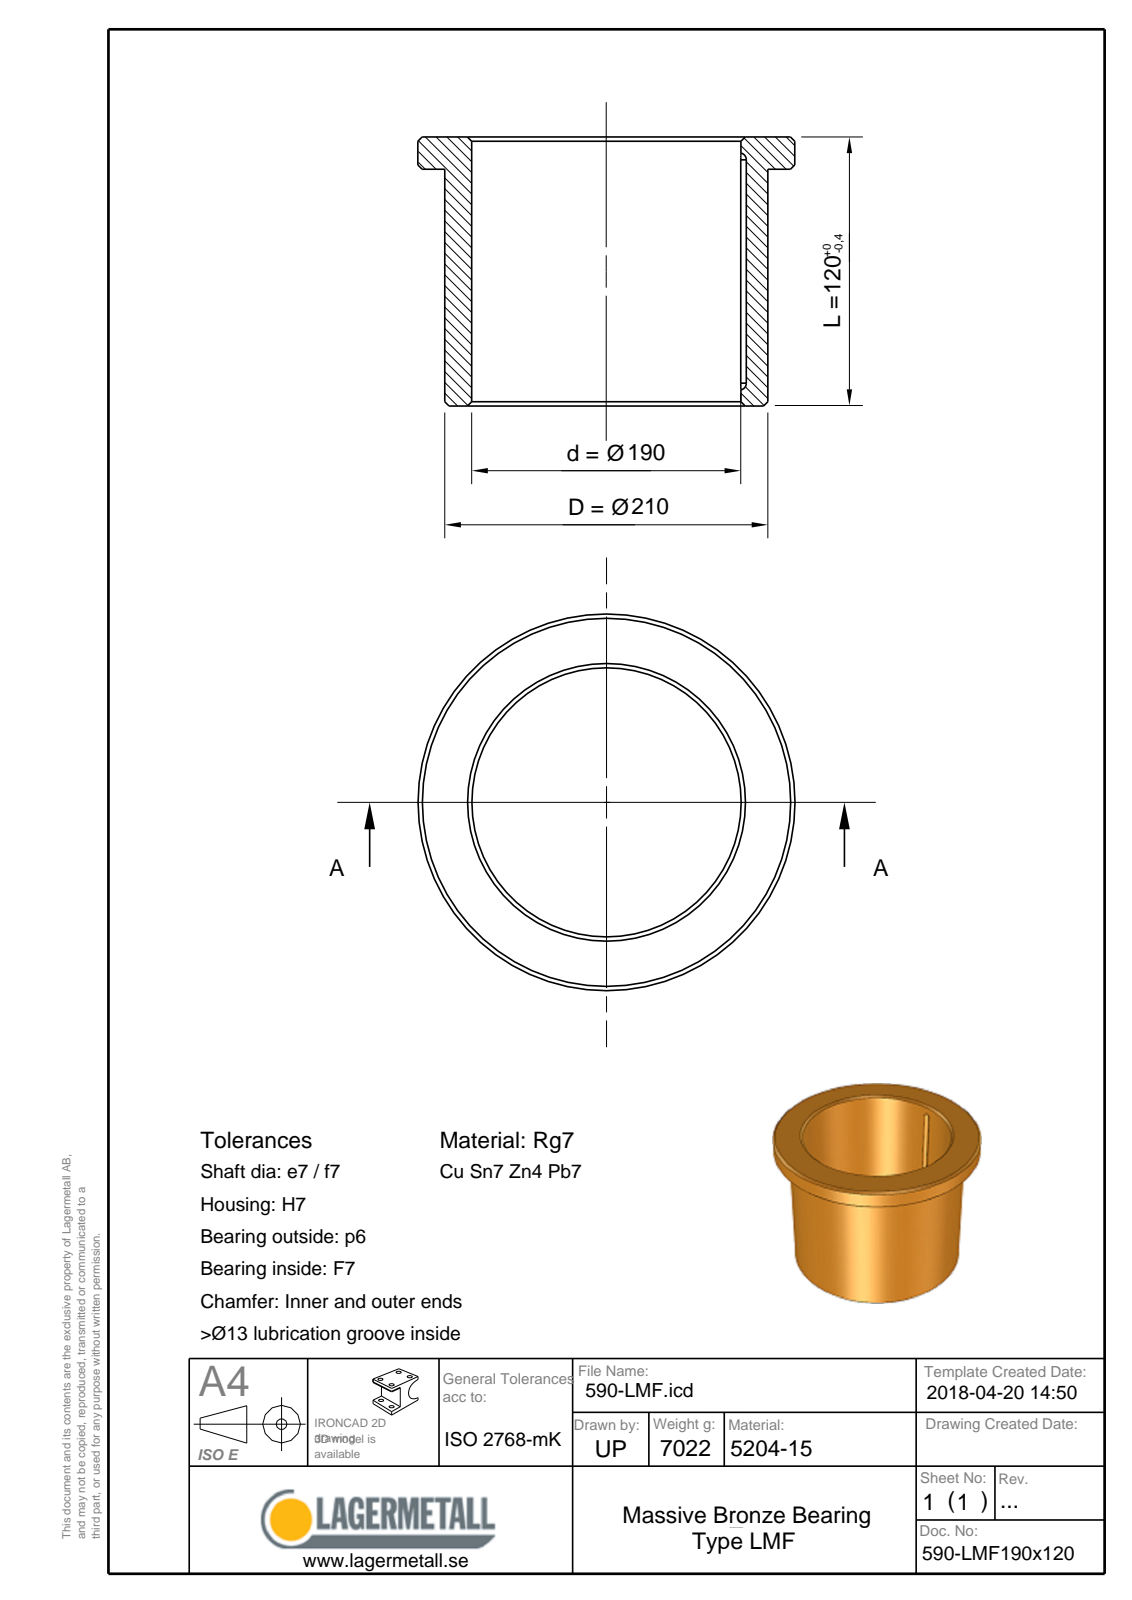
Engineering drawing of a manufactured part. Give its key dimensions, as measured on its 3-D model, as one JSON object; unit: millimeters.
{"part_name": "590-LMF190x120", "step_written_by": "Spatial InterOp 3D (CONFIG_CONTROL_DESIGN)", "units": "millimeters", "bodies": {"solids": 1, "faces": 16, "planar": 4, "cylindrical": 5, "other": 7}, "overall_size": [225, 225, 120], "volume_mm3": 797953, "surface_area_mm2": 170489, "round_holes": [[190, 1]], "round_bosses_or_shafts": [[225, 1], [210, 1]], "partial_cylinders_radius": [[2.25, 2]], "face_to_face_distances": [120, 110, 10]}
